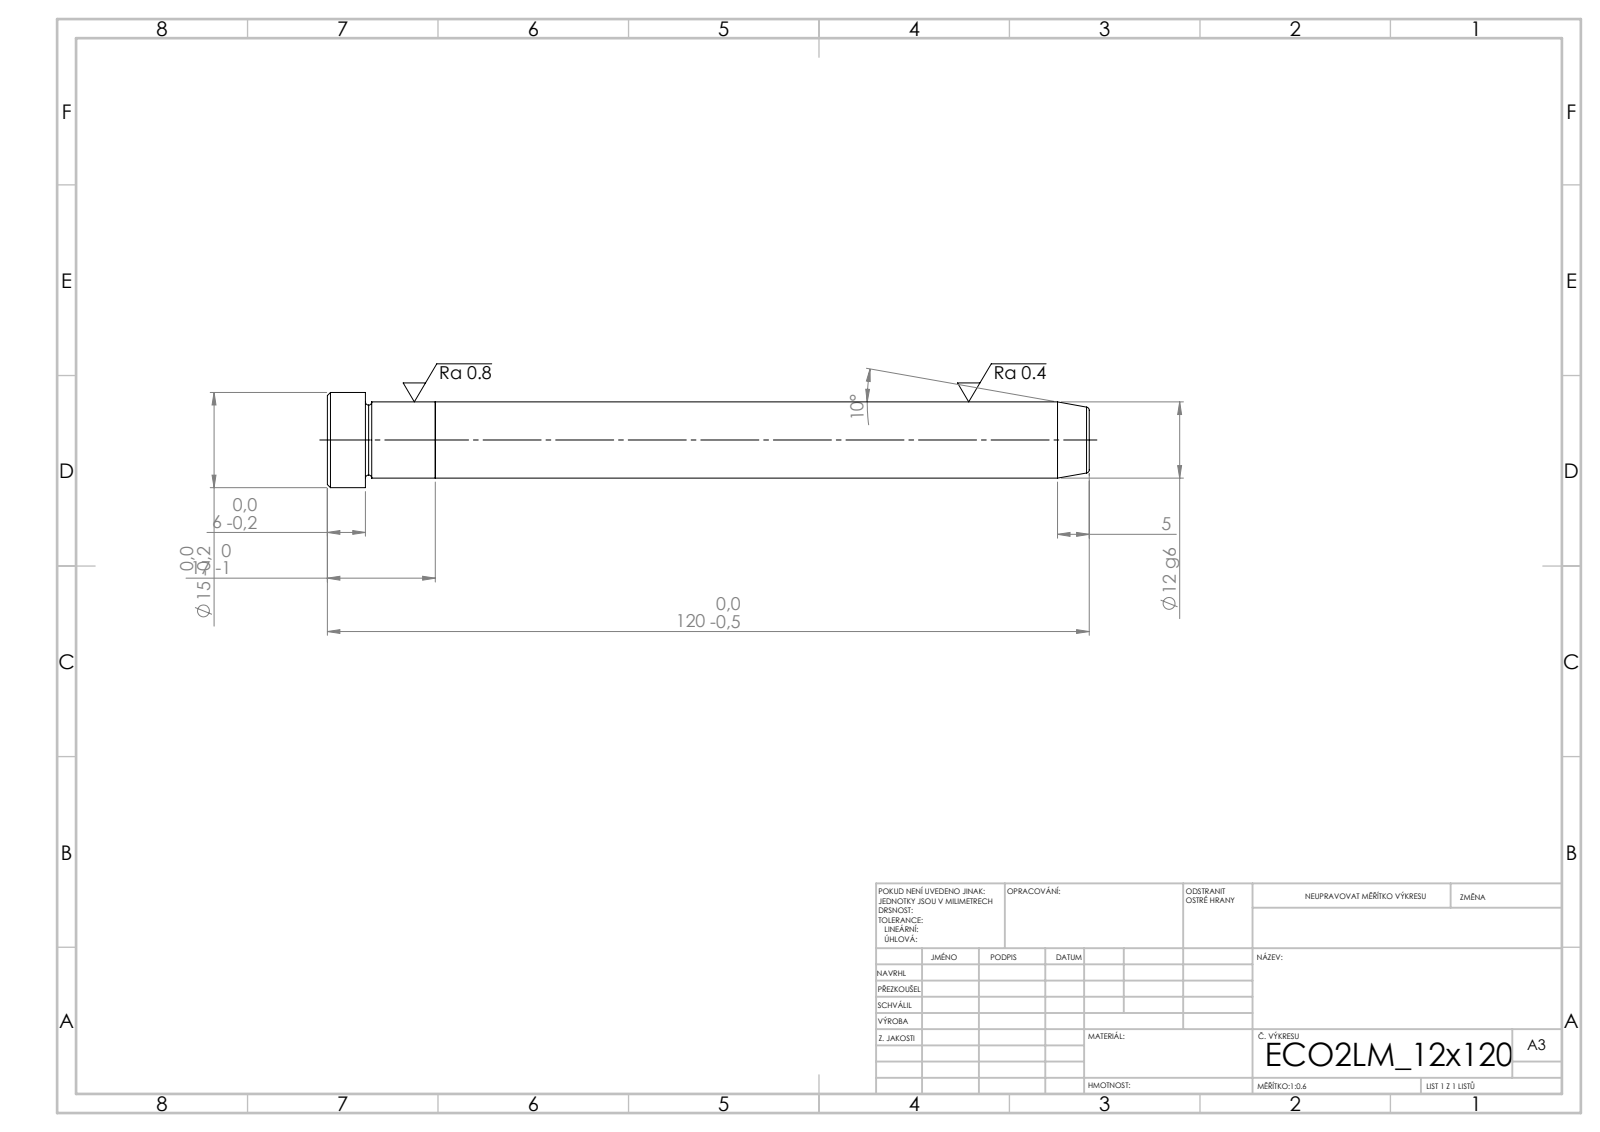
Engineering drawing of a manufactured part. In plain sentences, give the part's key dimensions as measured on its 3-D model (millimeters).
Its 3-D file was written by "SolidWorks 2019 (CONFIG_CONTROL_DESIGN)". It is 2 solids with 21 faces: 5 planar, 6 cylindrical and 10 other. Overall it measures 120 by 15 by 15 millimeters. Its volume is 13 853 cubic millimeters and its surface area 5 118 square millimeters. Round bosses or shafts: 1 of diameter 15, 1 of diameter 12. The main face-to-face distances are 17, 103, 120, 114, 11, 6.
